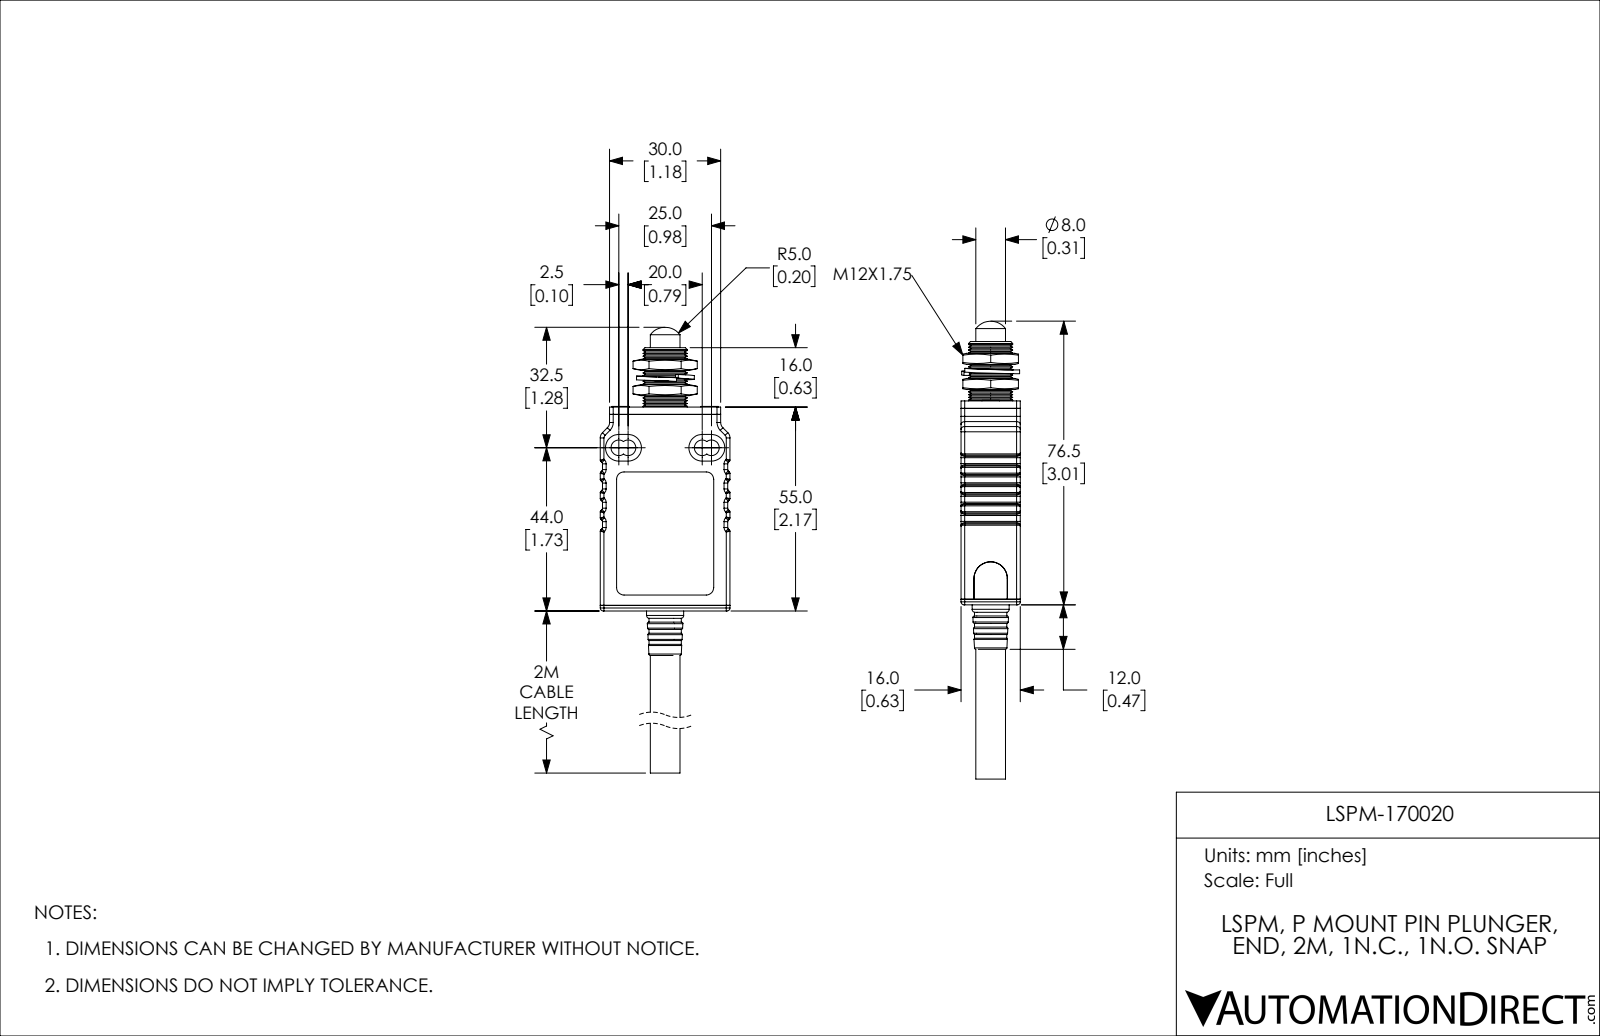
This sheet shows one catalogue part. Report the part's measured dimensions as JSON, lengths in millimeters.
{"part_name": "170-LSPM-Panel Mount Pin Plunger-Bottom Cable (STEP format)", "step_written_by": "SolidWorks 2013 (CONFIG_CONTROL_DESIGN)", "units": "millimeters", "bodies": {"solids": 13, "faces": 793, "planar": 248, "cylindrical": 295, "other": 250}, "overall_size": [123.5, 35, 16], "volume_mm3": 18694, "surface_area_mm2": 20536, "round_holes": [[2, 2], [2.5, 2], [2.6, 2], [4, 1], [5.4, 1], [8.2, 1], [9, 1], [11.2, 1], [12, 1], [13.5, 1], [14.6, 1]], "round_bosses_or_shafts": [[4.7, 2], [14.7, 1], [11.9, 1], [11, 1], [10.6, 1], [10, 1], [9.8, 1], [8.7, 1]], "partial_cylinders_radius": [[0.5, 74], [1, 52], [2, 8], [0.8, 4], [2.1, 4], [3.6, 4], [0.3, 3], [0.2, 2]], "face_to_face_distances": [1.5, 1, 15.7, 14.5, 1.2, 14.2, 2, 2.5, 13, 15.4], "hole_center_spacings": [12, 24]}
